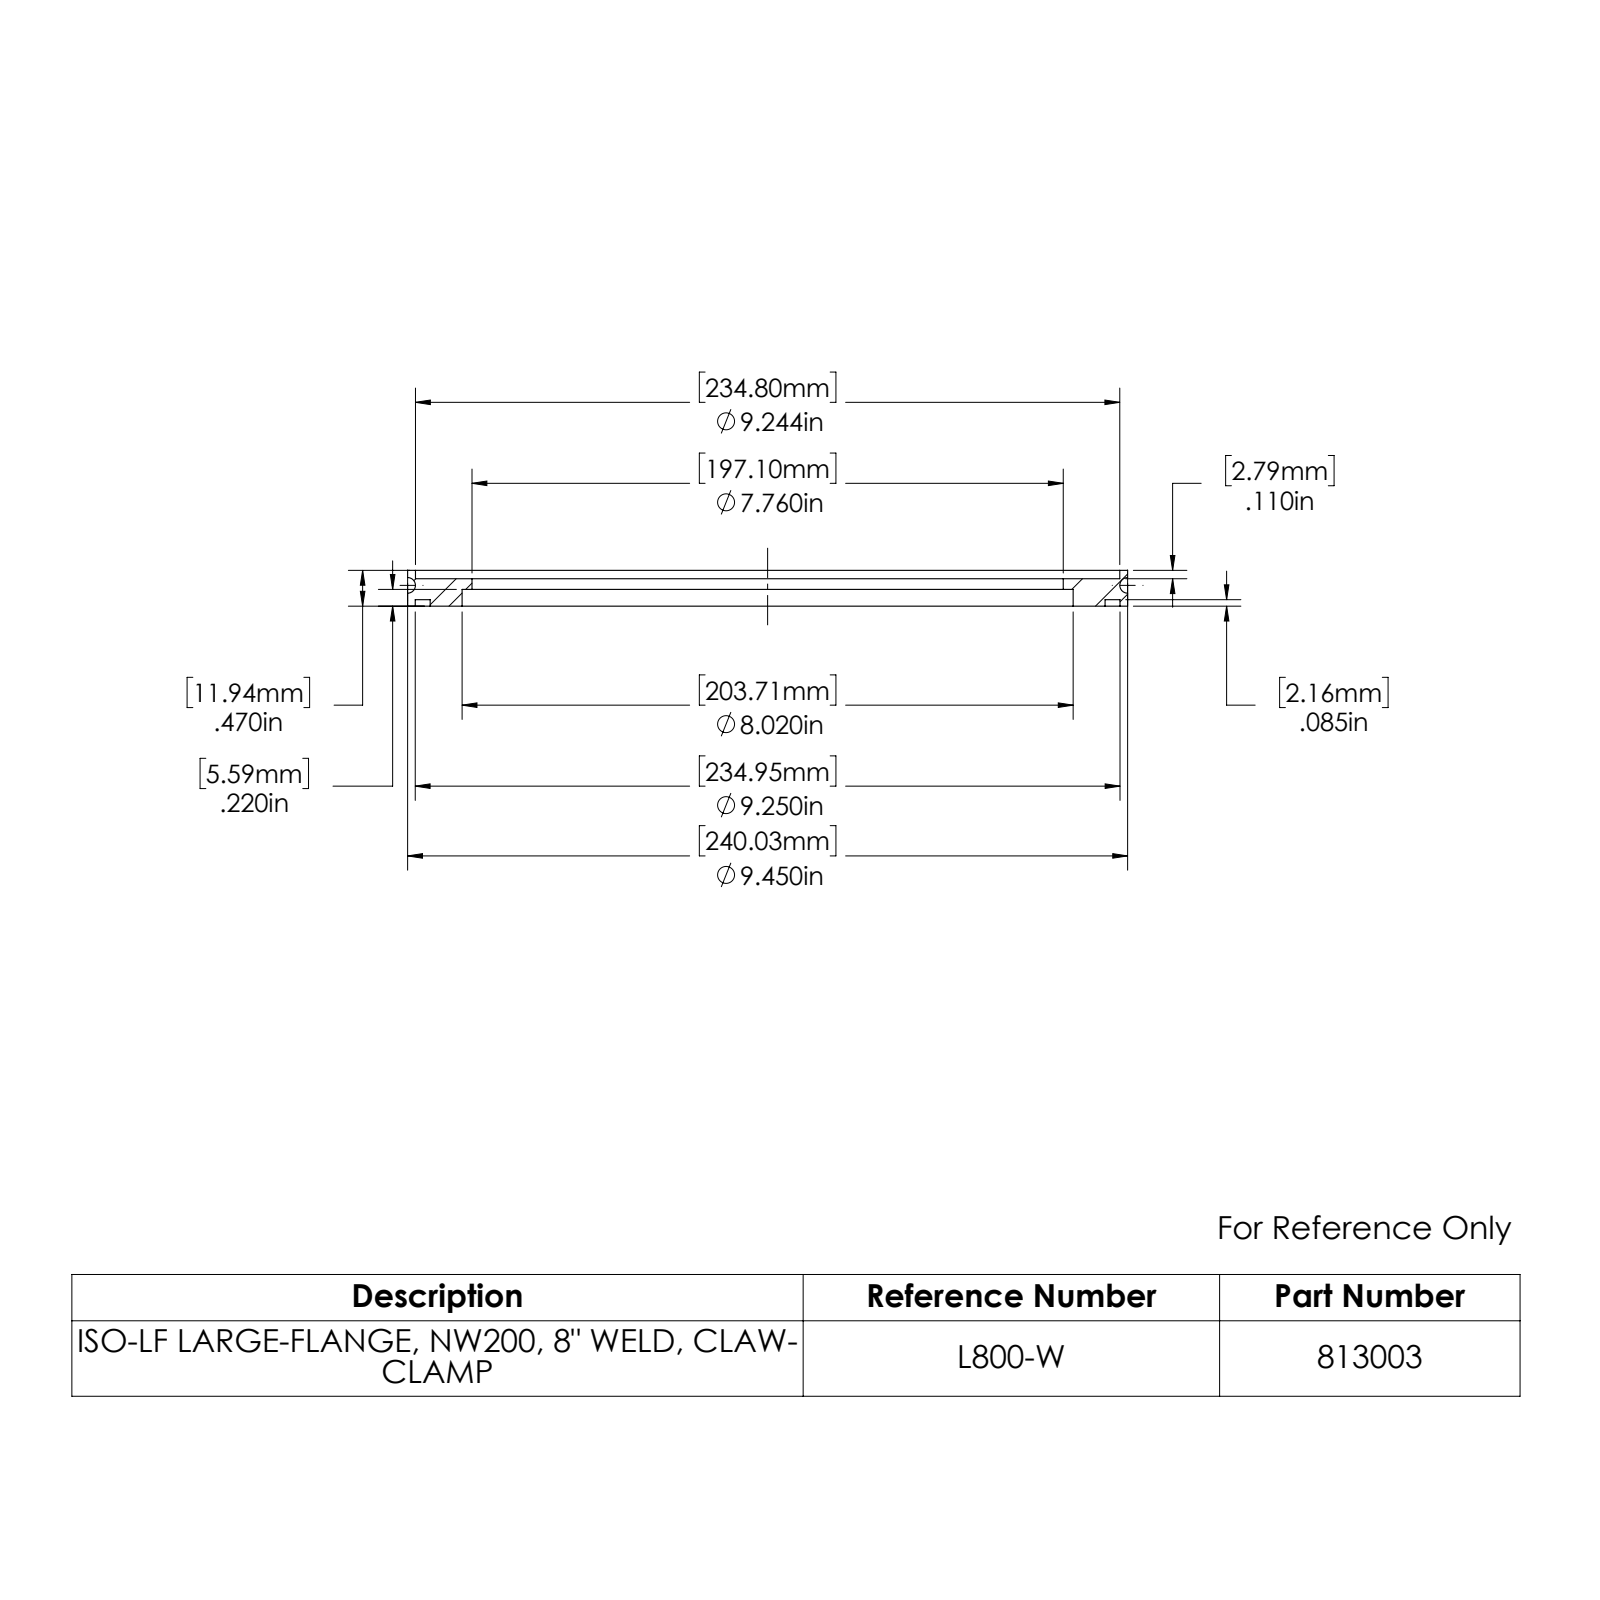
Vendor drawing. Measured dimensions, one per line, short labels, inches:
name: 813003
written by: SolidWorks 2022 (AUTOMOTIVE_DESIGN)
unit: in
bodies: 1 solid, 24 faces (6 planar, 14 cylindrical, 4 other)
size: 9.45 × 9.45 × 0.47
volume: 6.883 in³; area: 79.98 in²
holes: 1× ⌀7.76, 1× ⌀8.02, 1× ⌀9.244, 1× ⌀9.25
bosses: 1× ⌀9.45, 1× ⌀8.858
face distances: 0.36, 0.085, 0.275, 0.22, 0.135, 0.14, 0.47, 0.385, 0.25, 0.11
